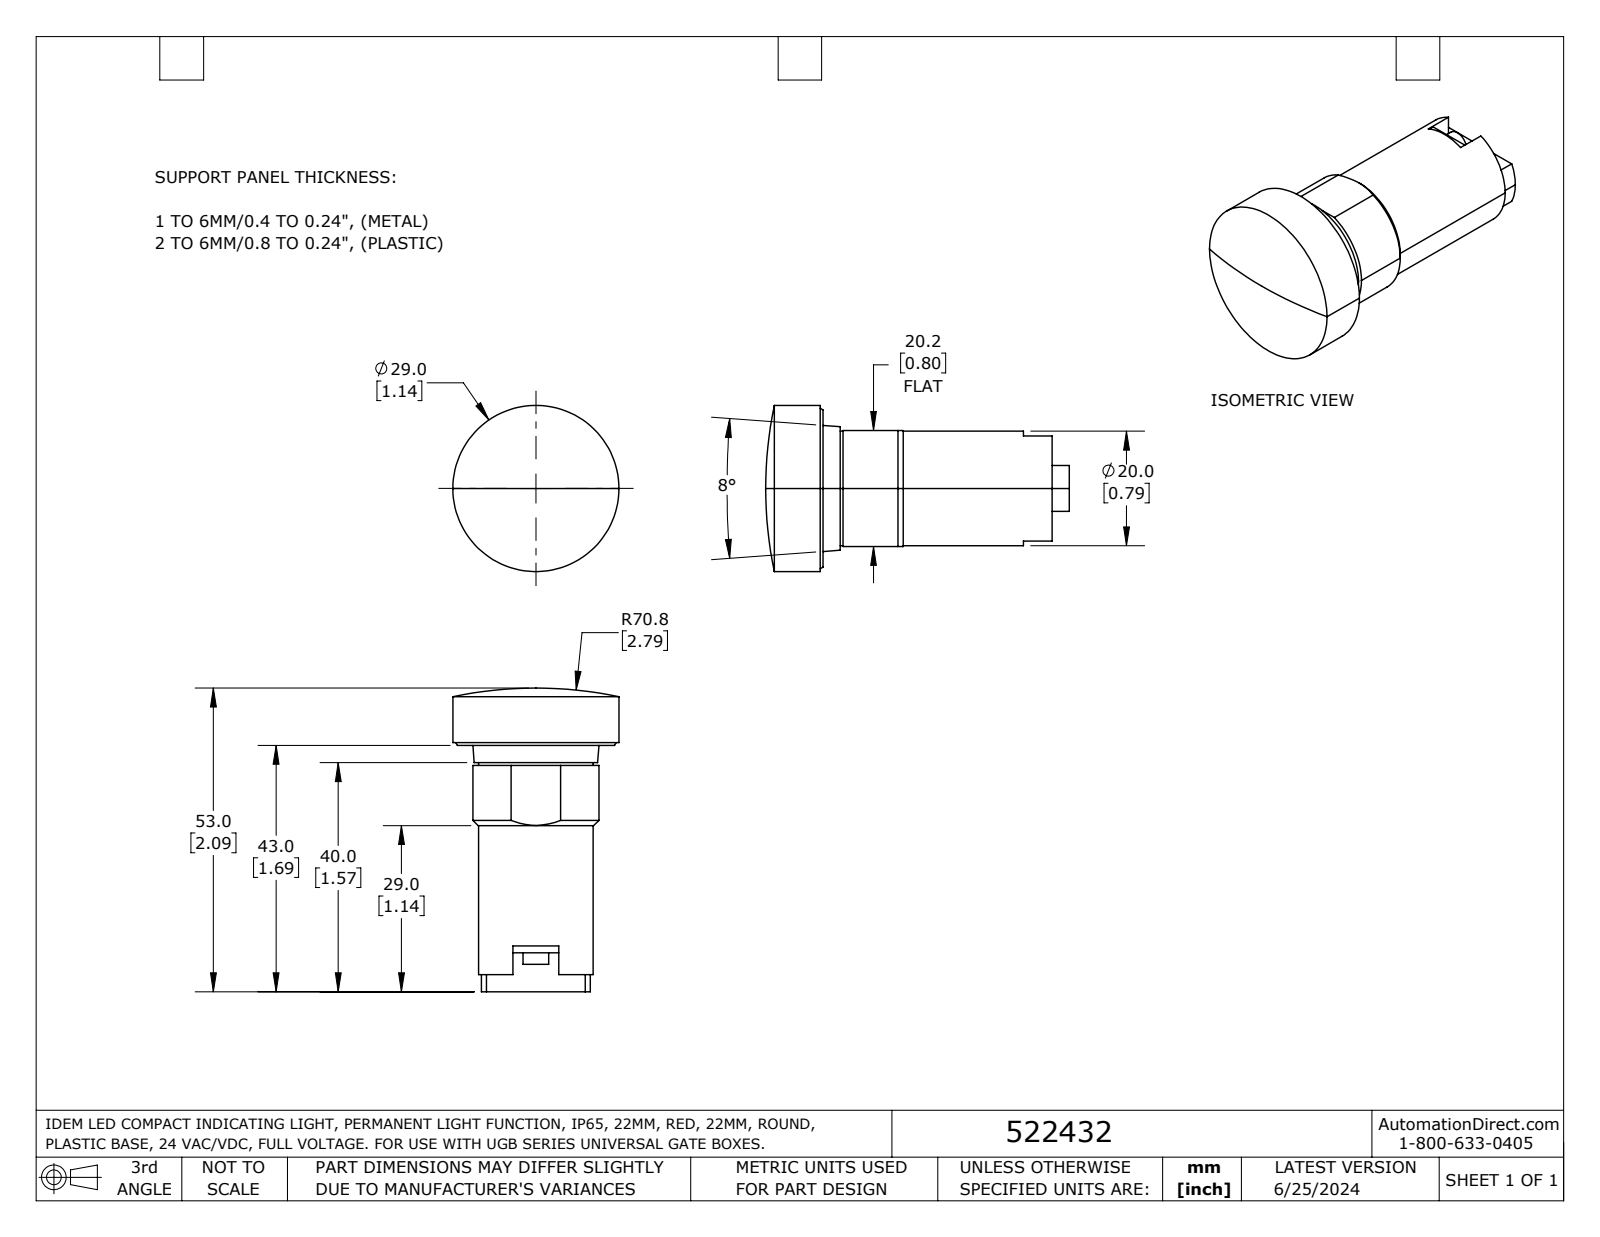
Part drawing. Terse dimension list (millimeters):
name: 522432
written by: SolidWorks 2023 (AUTOMOTIVE_DESIGN)
unit: mm
bodies: 1 solid, 50 faces (24 planar, 18 cylindrical, 8 other)
size: 53 × 29 × 29
volume: 19 530 mm³; area: 5 025 mm²
bosses: 2× ⌀4.5, 1× ⌀29, 1× ⌀20
rounds: 1× R9.5, 1× R11
face distances: 6.1, 14.1, 43, 8, 3, 40, 3.5, 0.5, 20.2, 36.5
